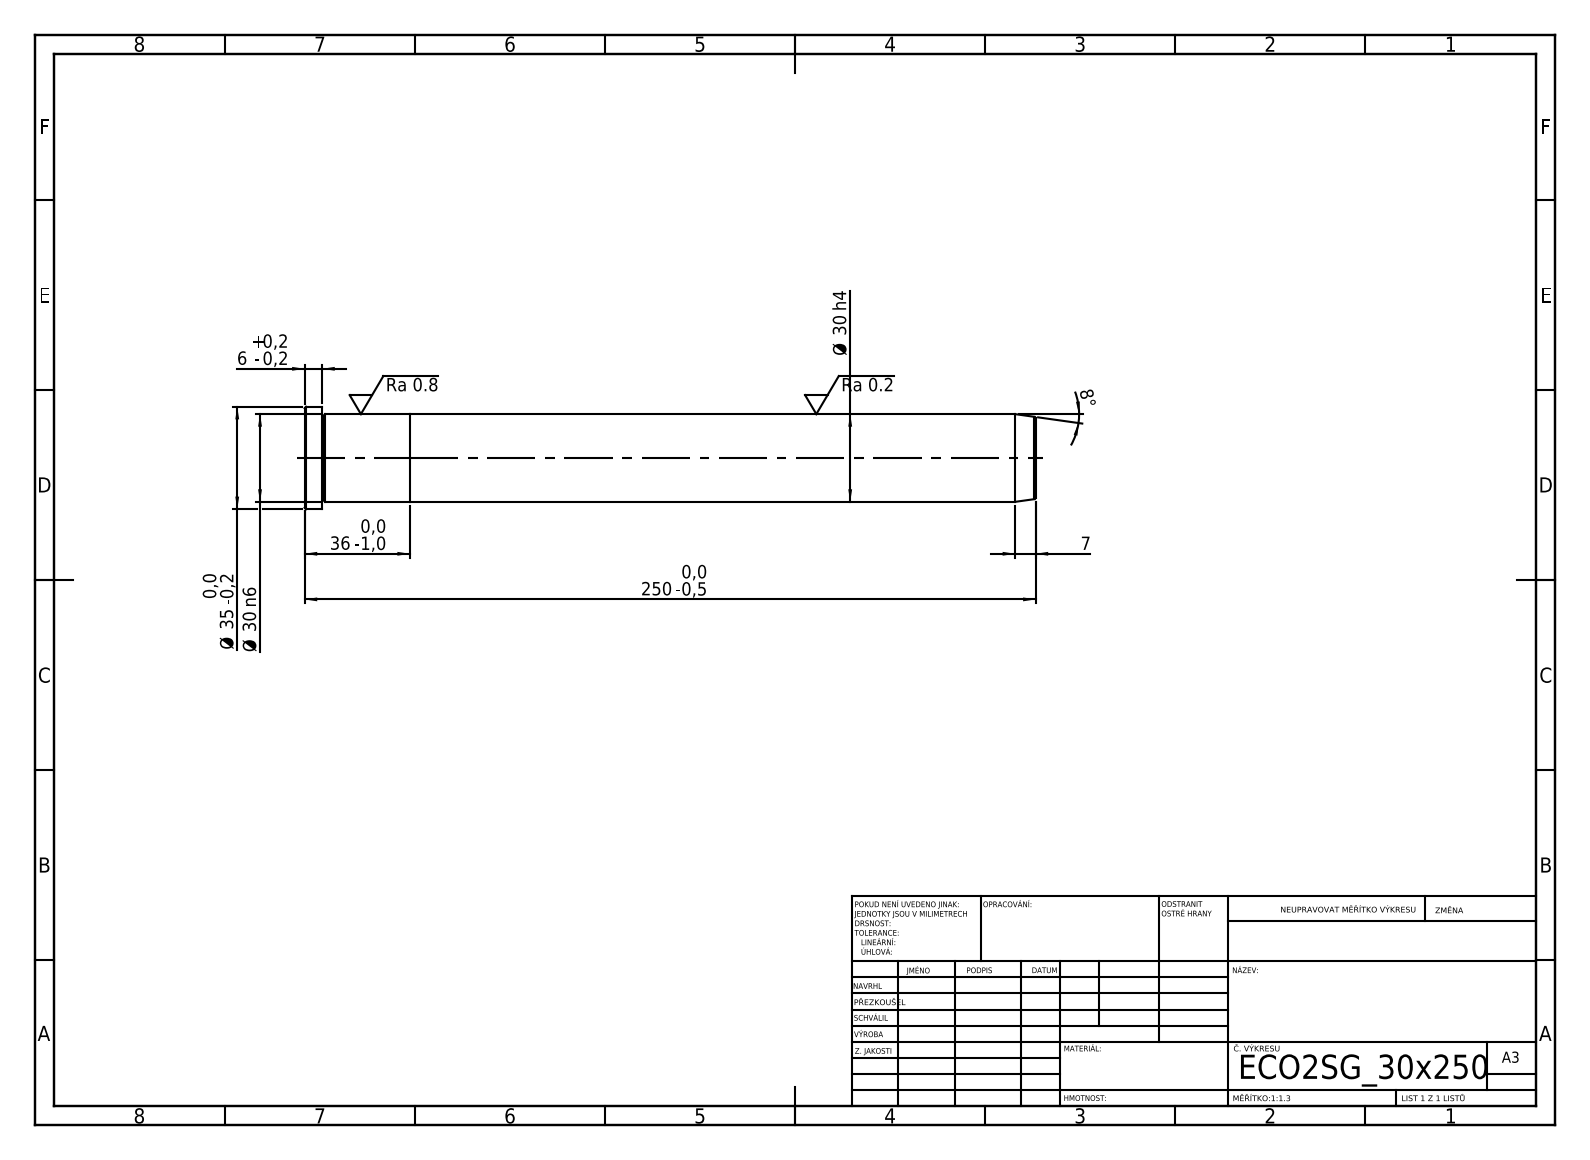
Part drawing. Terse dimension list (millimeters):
written by: SolidWorks 2019 (CONFIG_CONTROL_DESIGN)
unit: mm
bodies: 2 solids, 21 faces (5 planar, 6 cylindrical, 10 other)
size: 250 × 35 × 35
volume: 177 875 mm³; area: 26 894 mm²
bosses: 1× ⌀35, 1× ⌀30
face distances: 36, 214, 250, 244, 30, 6
